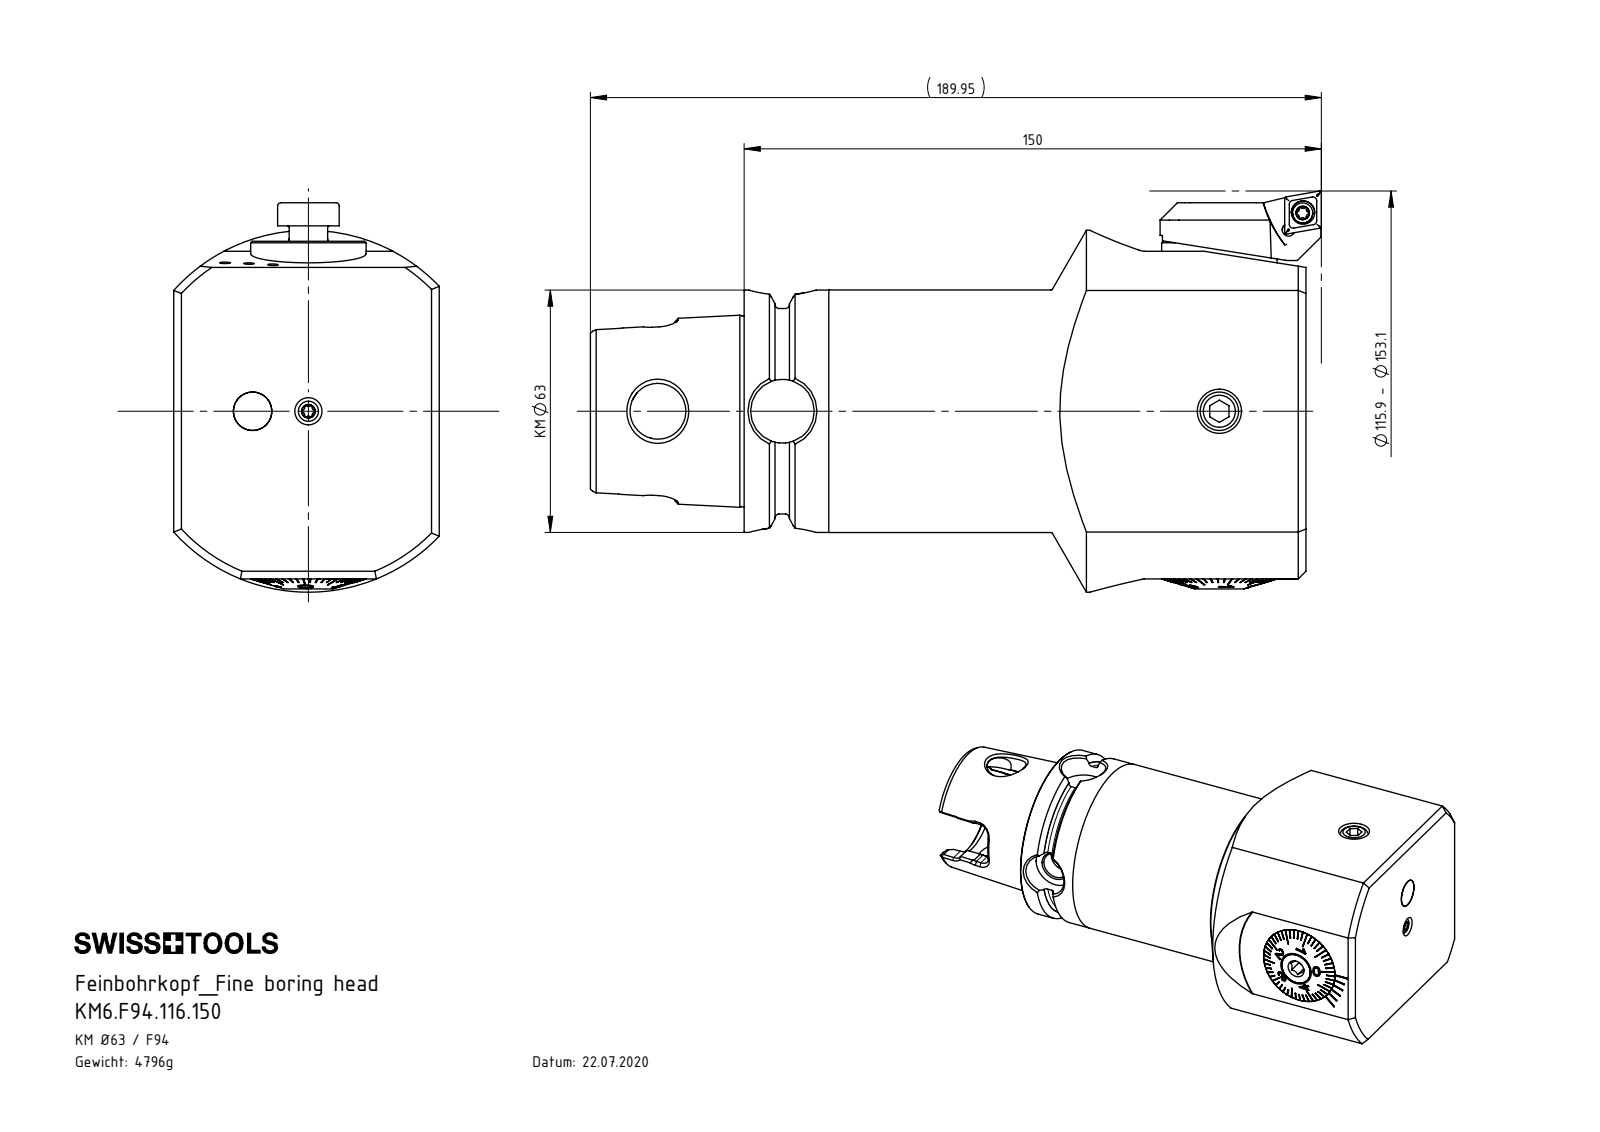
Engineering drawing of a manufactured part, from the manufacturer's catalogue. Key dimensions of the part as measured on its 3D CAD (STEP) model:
Part name (STEP PRODUCT): A55-BG3.011.033_A_gekrzt; F55-BG1.012.012_A; A55-BG2.013.005_C; F94-BG1.DA3.030_A (+8 more)
STEP written by: SolidWorks 2017 (AUTOMOTIVE_DESIGN)
Units: millimetres
Bodies: 13 solids, 720 faces (348 planar, 110 cylindrical, 262 other)
Overall size (bounding box): 185.95 × 101.15 × 69
Volume: 613 706 mm³ · Surface area: 89 624 mm²
Round holes (diameter × count): ⌀2.5 ×3, ⌀4.2 ×3, ⌀3.3 ×2, ⌀8.5 ×2, ⌀5 ×1, ⌀8 ×1, ⌀10 ×1, ⌀10.1 ×1, ⌀10.2 ×1, ⌀11.4 ×1, ⌀12 ×1, ⌀12.1 ×1
Round bosses / shafts (diameter × count): ⌀10 ×2, ⌀63 ×1, ⌀62.95 ×1, ⌀30 ×1, ⌀29.98 ×1, ⌀29.9 ×1, ⌀25 ×1, ⌀18 ×1
Partial cylindrical surfaces — rounded edges, fillets, slot ends (radius × count): R0.34 ×6, R0.59 ×6, R2.5 ×6, R4 ×6, R2 ×4, R3.2 ×3, R0.5 ×2, R7.04 ×2
Main face-to-face distances: 69, 6.5, 146, 1.1, 78.6, 85.1, 147.1, 2.6, 87.7, 2.5
Hole centre spacings: 113.55, 14.5, 32.35, 145.9
